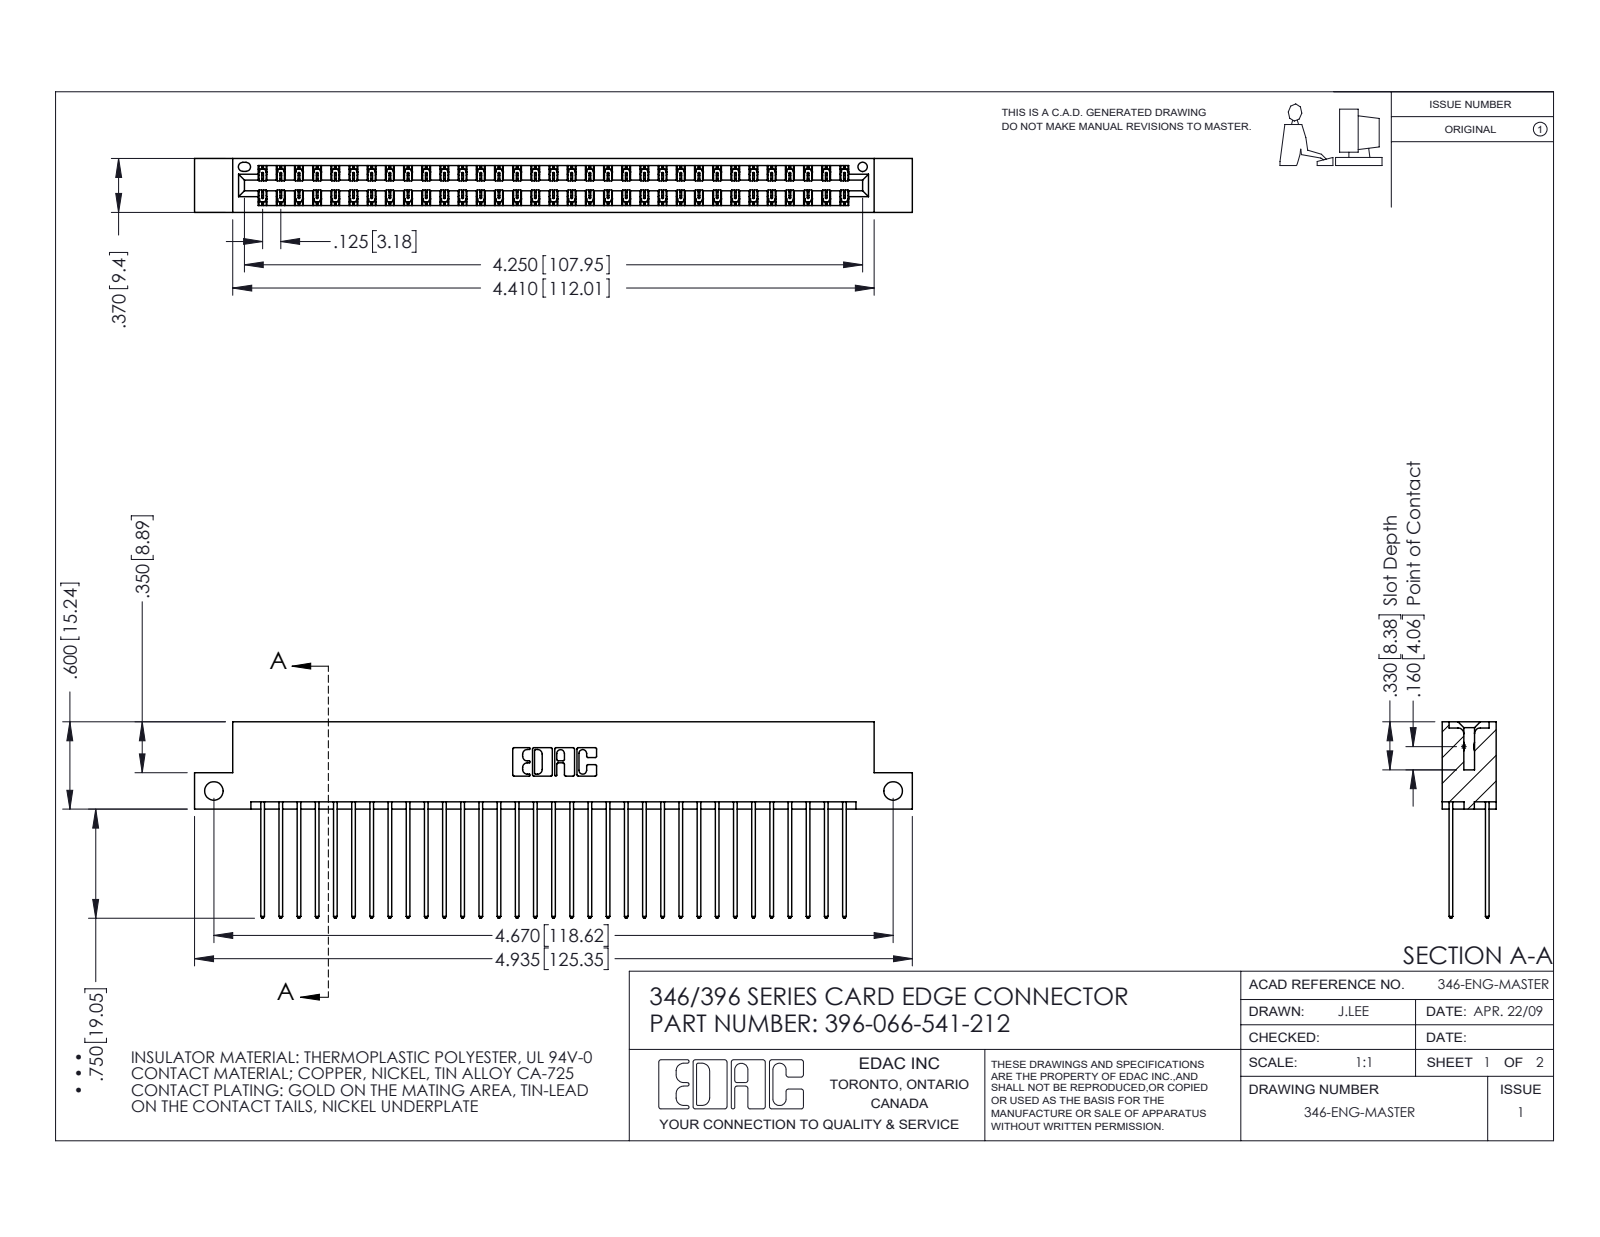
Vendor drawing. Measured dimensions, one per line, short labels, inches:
name: 345-292-001_345-293-141; 346 Part_Flush Mounting Lugs - Side Mount; 396-066-541-212
written by: SolidWorks 2016 (CONFIG_CONTROL_DESIGN)
unit: in
bodies: 67 solids, 3554 faces (2386 planar, 1168 cylindrical, 0 other)
size: 4.935 × 1.35 × 0.37
volume: 0.759 in³; area: 28.9 in²
holes: 2× ⌀0.128, 1× ⌀0.064
rounds: 99× R0.006, 66× R0.01, 22× R0.01, 6× R0.007, 6× R0.031, 3× R0.026, 2× R0.014, 2× R0.022
face distances: 0.048, 0.322, 0.25, 0.072, 0.298, 0.025, 0.37, 0.275, 0.225, 0.148
hole spacings: 4.67
